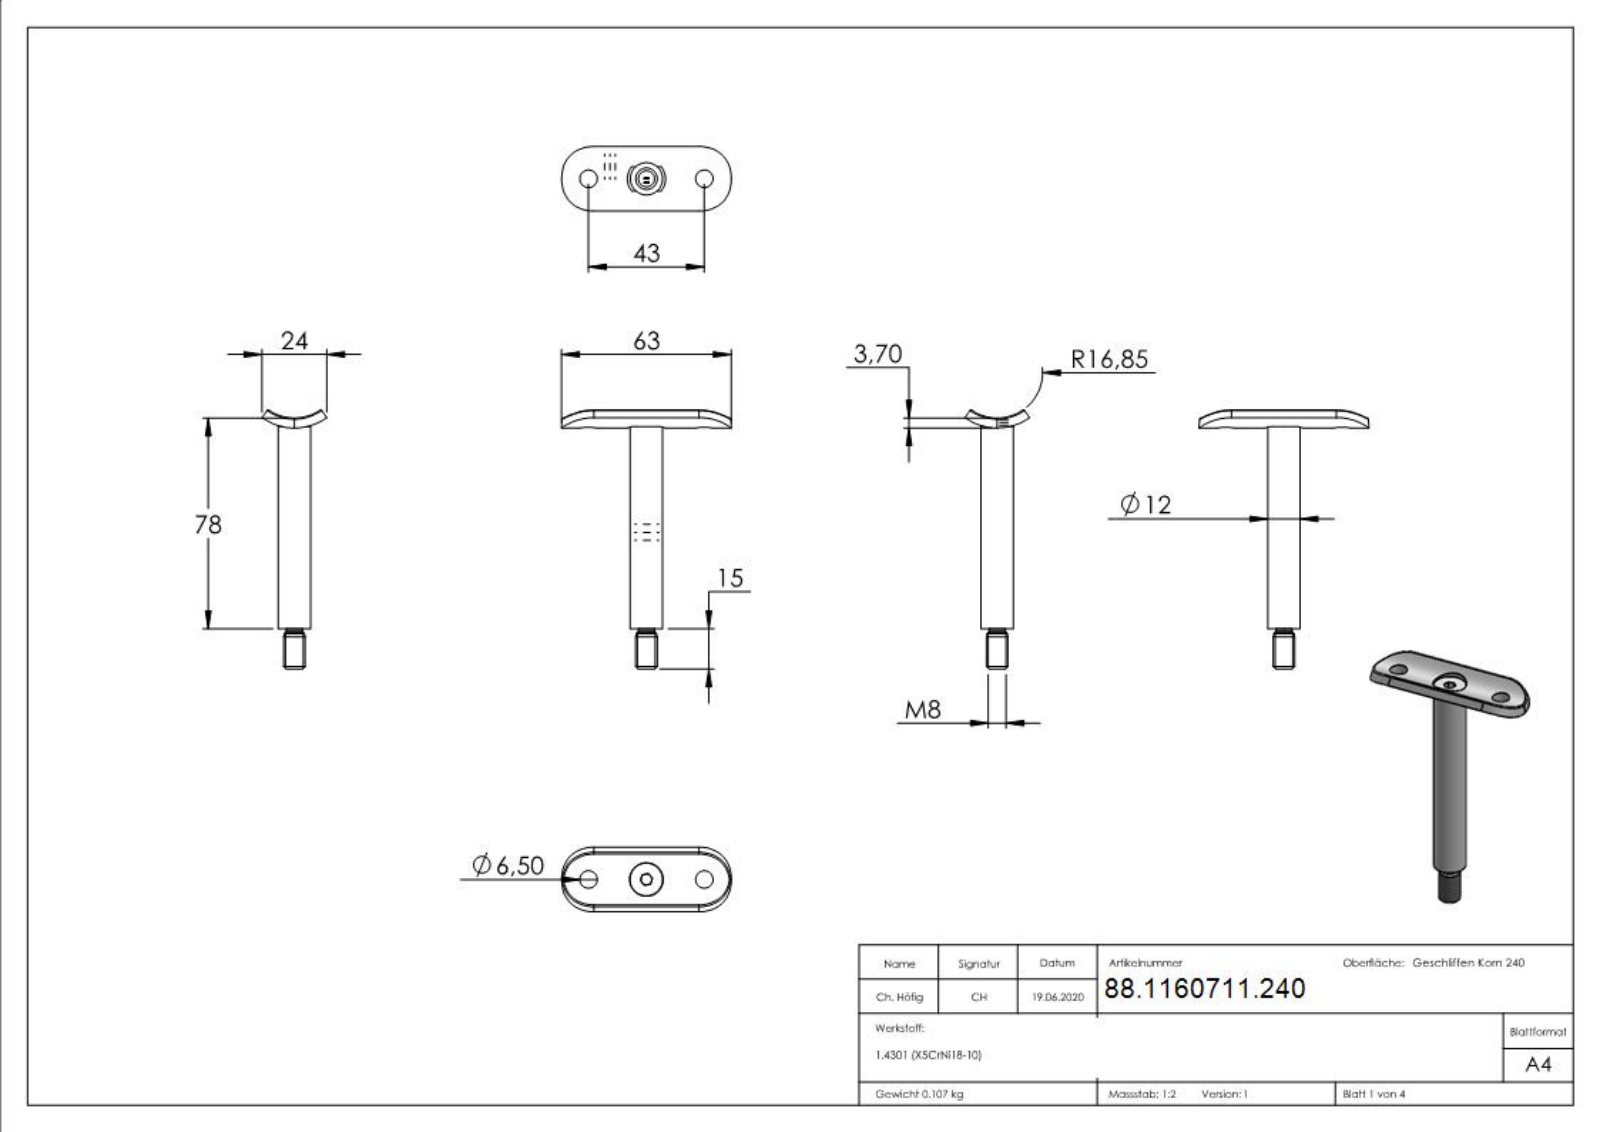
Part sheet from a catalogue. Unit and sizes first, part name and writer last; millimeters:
Units: millimetres
Overall size (bounding box): 96.18 × 63 × 24
Round holes (diameter × count): ⌀6.5 ×2, ⌀5 ×1, ⌀8 ×1, ⌀12.5 ×1
Round bosses / shafts (diameter × count): ⌀12 ×1, ⌀6 ×1
Partial cylindrical surfaces — rounded edges, fillets, slot ends (radius × count): R12 ×4, R0.5 ×2, R7.1 ×1, R16.85 ×1, R20.55 ×1
Main face-to-face distances: 2.7, 90, 92.7, 4, 80.7, 9.3, 12, 89.7, 9, 3
Hole centre spacings: 21.5, 43
Volume: 13 500 mm³ · Surface area: 7 442 mm²
Bodies: 3 solids, 289 faces (136 planar, 31 cylindrical, 122 other)
Part name (STEP PRODUCT): 60181-240_60181-240; DIN-7991_-_DIN7991 M6x16_DIN7991 M6x12; 60711-240; 50236-Konfig_50236-240-75-M6
STEP written by: SolidWorks 2015 (CONFIG_CONTROL_DESIGN)
